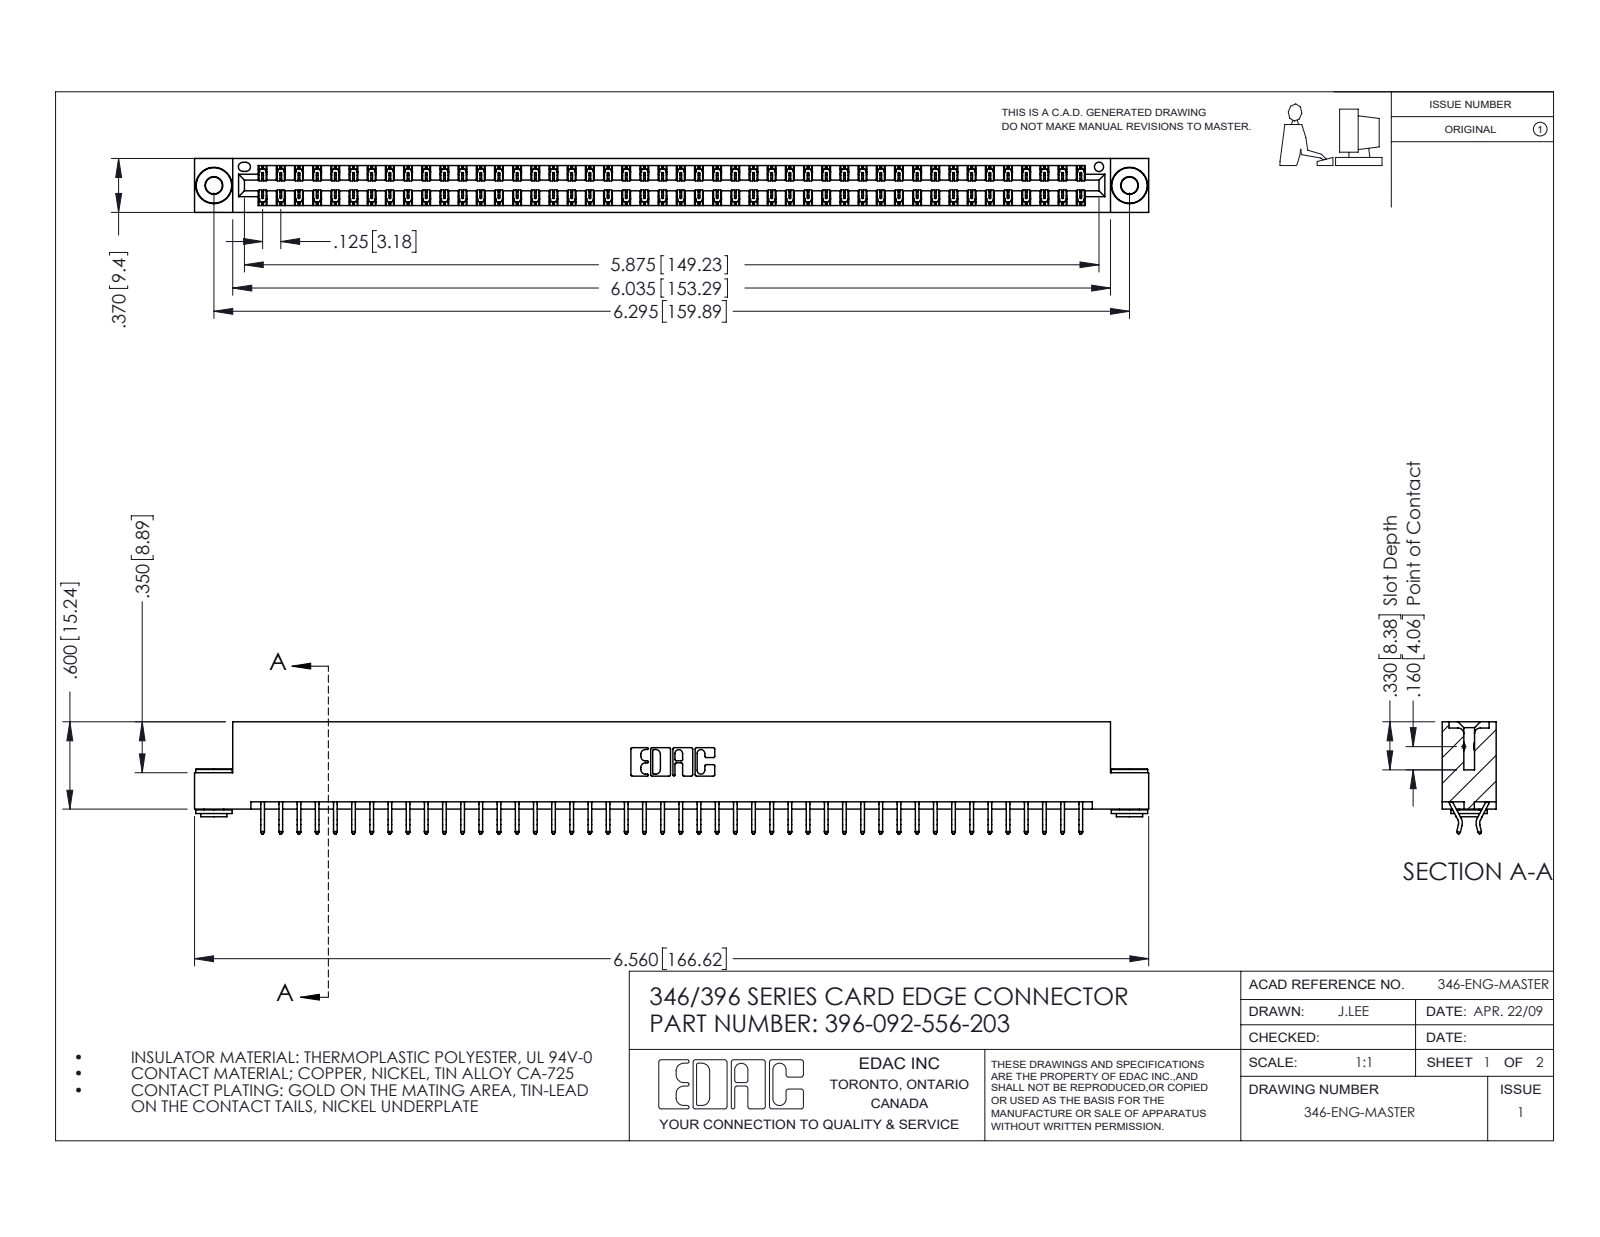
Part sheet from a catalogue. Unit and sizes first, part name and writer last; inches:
Units: inches
Overall size (bounding box): 6.56 × 0.77 × 0.37
Round holes (diameter × count): ⌀0.116 ×2, ⌀0.156 ×2, ⌀0.064 ×1
Round bosses / shafts (diameter × count): ⌀0.25 ×2, ⌀0.18 ×2, ⌀0.136 ×2
Partial cylindrical surfaces — rounded edges, fillets, slot ends (radius × count): R0.006 ×138, R0.01 ×22, R0.007 ×6, R0.031 ×6, R0.026 ×3, R0.01 ×2, R0.014 ×2, R0.022 ×2
Main face-to-face distances: 0.048, 0.322, 0.37, 0.25, 0.025, 0.072, 0.298, 0.275, 0.148, 0.222
Hole centre spacings: 0.246, 6.086, 6.295
Volume: 0.994 in³ · Surface area: 35.01 in²
Bodies: 95 solids, 5496 faces (3674 planar, 1814 cylindrical, 8 other)
Part name (STEP PRODUCT): 396-092-556-203; 345-250-002_345-250-002-102; 345-292-001_556 Tail; 346 Part_Flush Mounting Lugs - 0.156 Dia-TH
STEP written by: SolidWorks 2016 (CONFIG_CONTROL_DESIGN)
